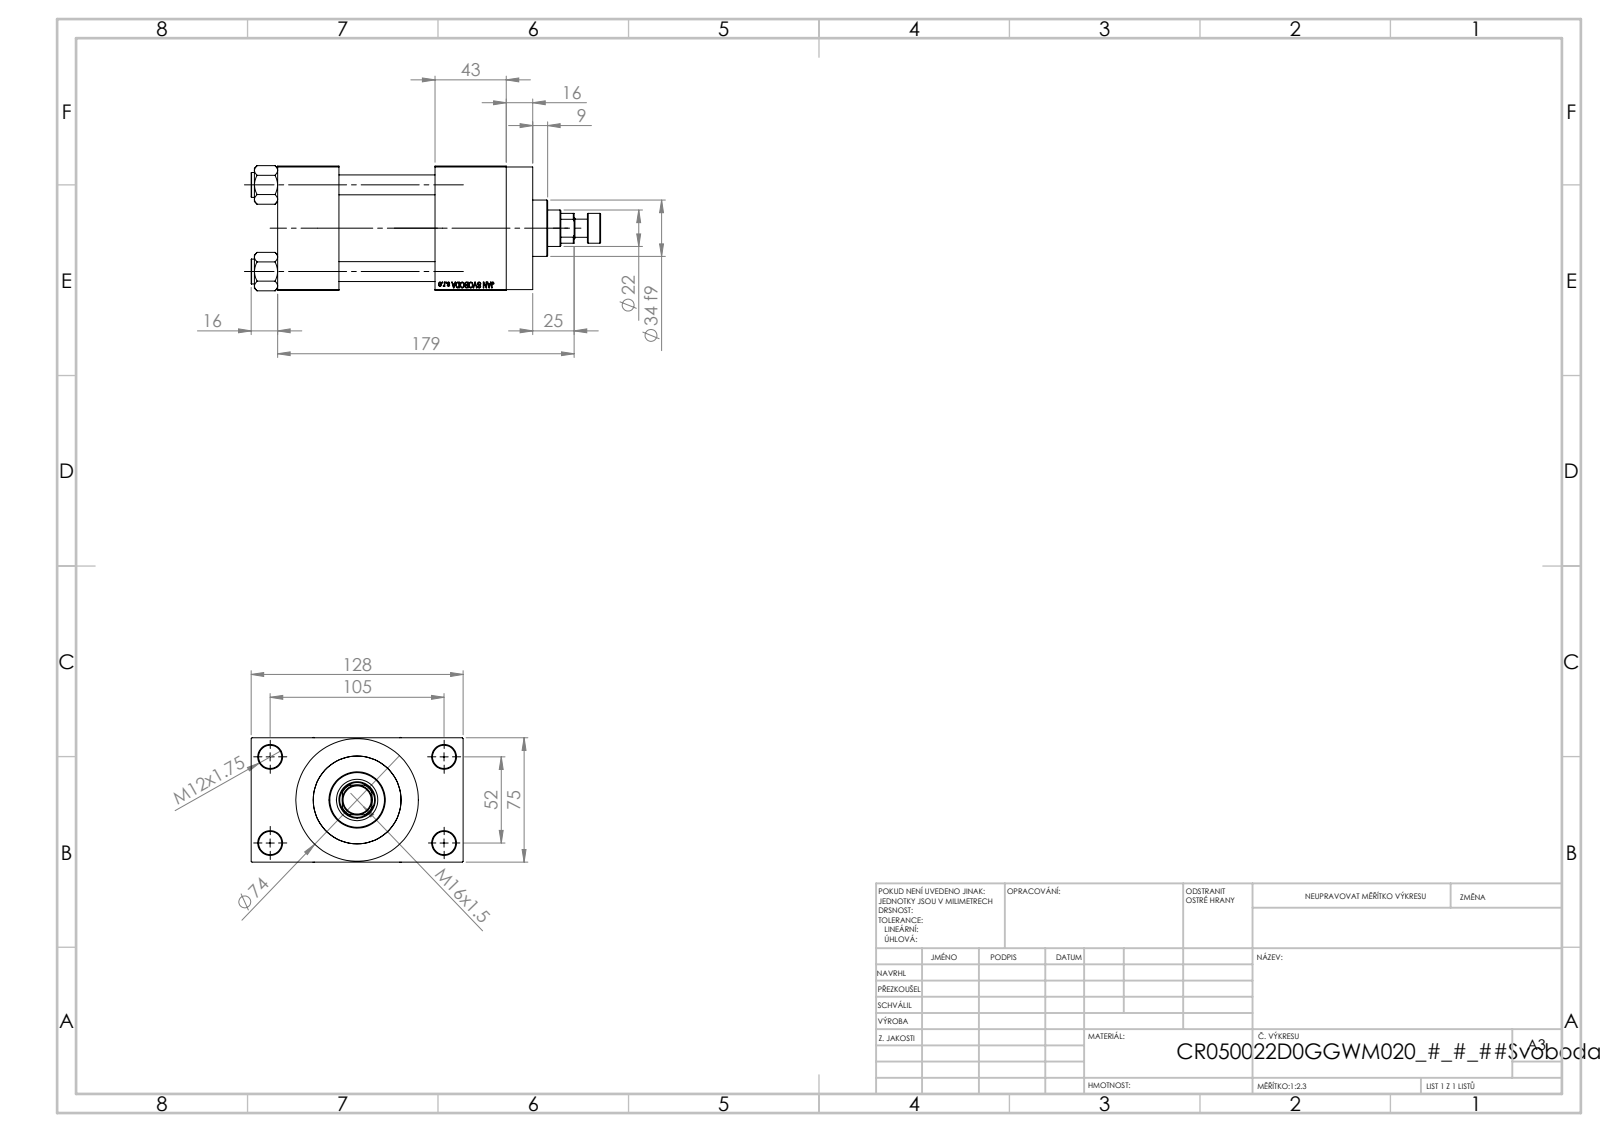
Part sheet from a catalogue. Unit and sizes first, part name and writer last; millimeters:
Units: millimetres
Overall size (bounding box): 211 × 128 × 75.54
Round holes (diameter × count): ⌀12 ×4, ⌀14 ×4, ⌀7 ×2, ⌀20.96 ×2, ⌀30 ×2, ⌀10.5 ×1, ⌀22 ×1, ⌀25 ×1, ⌀41 ×1, ⌀50 ×1, ⌀53 ×1
Round bosses / shafts (diameter × count): ⌀15 ×4, ⌀74 ×1, ⌀56 ×1, ⌀34 ×1, ⌀18 ×1, ⌀11 ×1
Partial cylindrical surfaces — rounded edges, fillets, slot ends (radius × count): R10.5 ×1
Main face-to-face distances: 75, 58, 37, 95, 26.5, 101.5, 138, 101, 43, 16
Hole centre spacings: 26.35, 36.98, 52.3, 58.43, 58.59, 78.65, 94.37, 52
Volume: 809 343 mm³ · Surface area: 166 227 mm²
Bodies: 12 solids, 1118 faces (501 planar, 93 cylindrical, 524 other)
Part name (STEP PRODUCT): V215CR_ROD_END_W; V215CR_D_TYCINKA; V215CR_VCP_D; V215CR_D_Body (+2 more)
STEP written by: SolidWorks 2019 (CONFIG_CONTROL_DESIGN)
